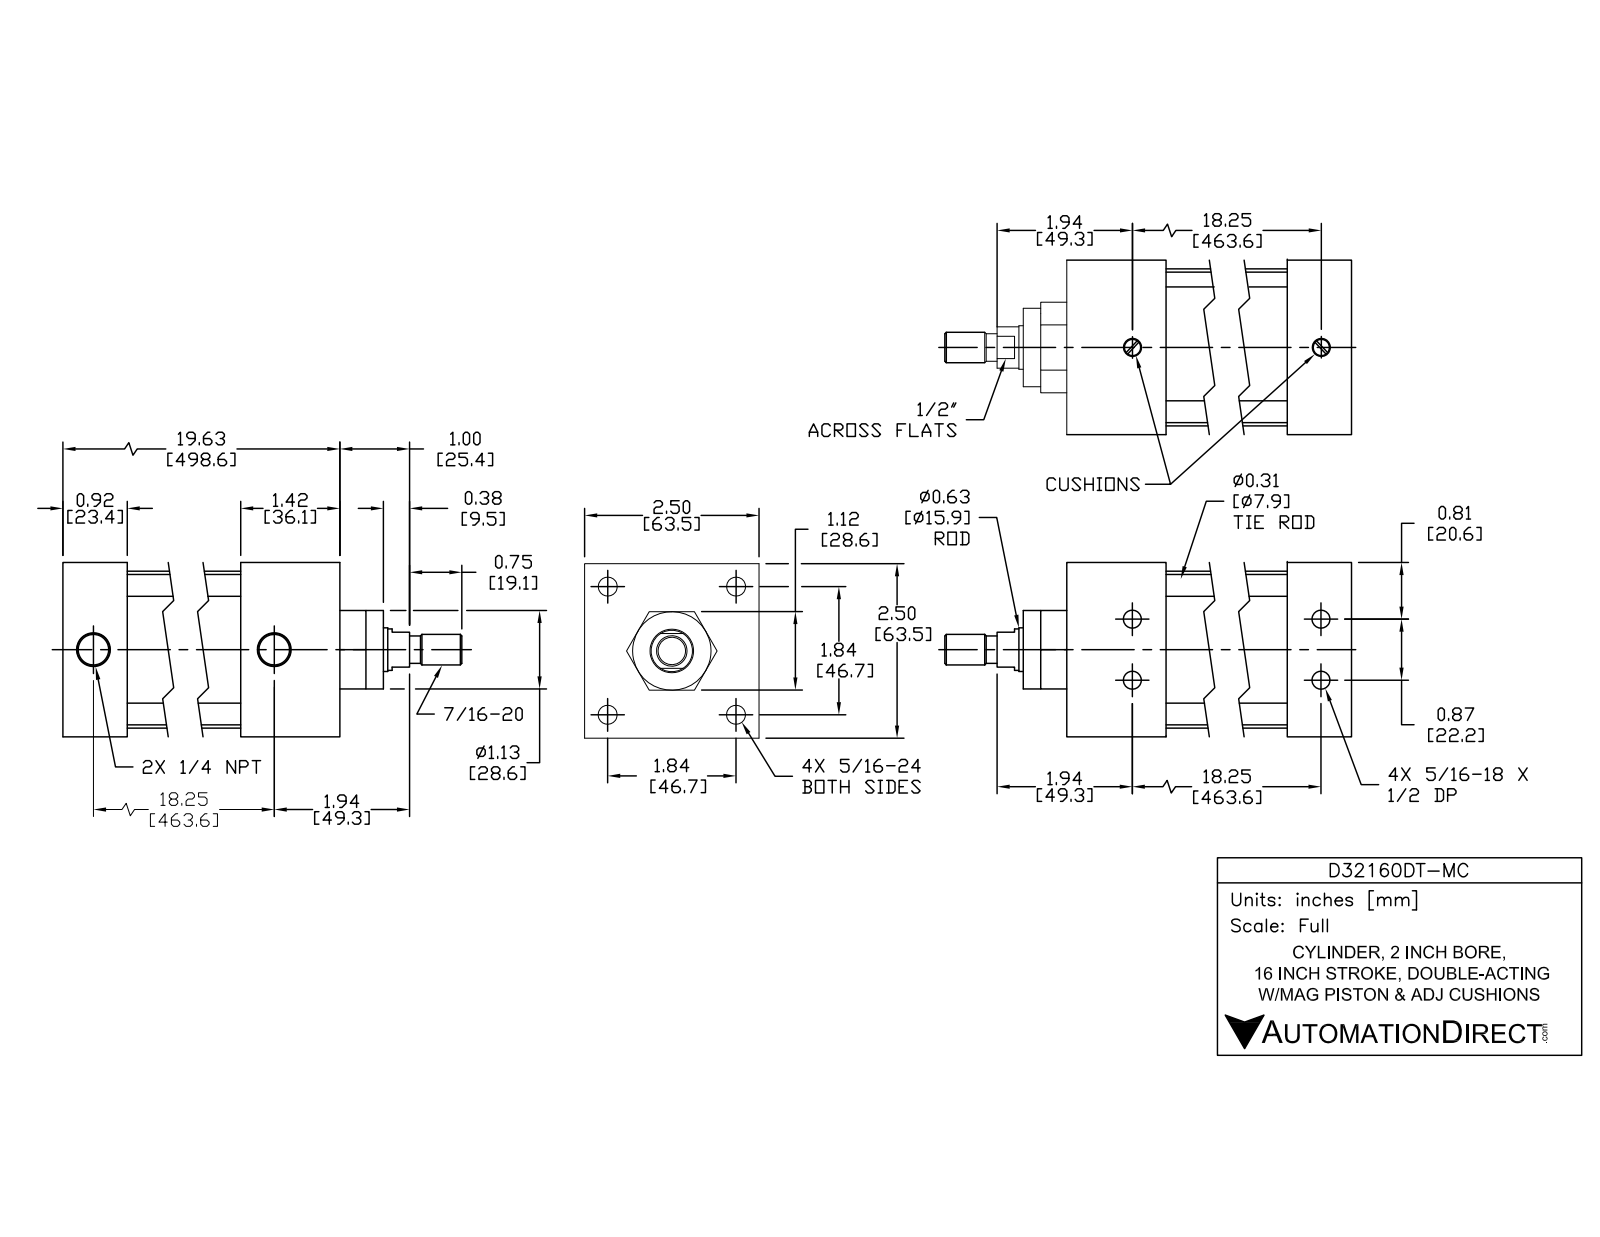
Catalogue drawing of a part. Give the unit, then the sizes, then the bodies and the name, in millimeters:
Units: millimetres
Overall size (bounding box): 542.8 × 63.5 × 63.5
Round holes (diameter × count): ⌀6.4 ×4, ⌀6.8 ×4, ⌀9.1 ×4, ⌀12.7 ×4, ⌀7.5 ×2, ⌀12.1 ×2, ⌀15.9 ×1, ⌀16 ×1, ⌀50.8 ×1
Round bosses / shafts (diameter × count): ⌀12.3 ×4, ⌀8 ×4, ⌀7.2 ×4, ⌀57.2 ×1, ⌀50.7 ×1, ⌀28.4 ×1, ⌀15.8 ×1, ⌀15 ×1
Partial cylindrical surfaces — rounded edges, fillets, slot ends (radius × count): R6.4 ×4
Main face-to-face distances: 63.5, 498.4, 36.1, 462.3, 438.9, 475, 23.4, 25.4, 472.5, 436.4
Hole centre spacings: 11.1, 33.2, 46.9, 463.6, 463.4, 22.2, 66.4, 464
Volume: 689 100 mm³ · Surface area: 274 300 mm²
Bodies: 12 solids, 298 faces (94 planar, 114 cylindrical, 90 other)
Part name (STEP PRODUCT): D32160DT-MC; D32160DT-M PISTON; D32160DT-M BODY
STEP written by: SolidWorks 2015 (AUTOMOTIVE_DESIGN)
